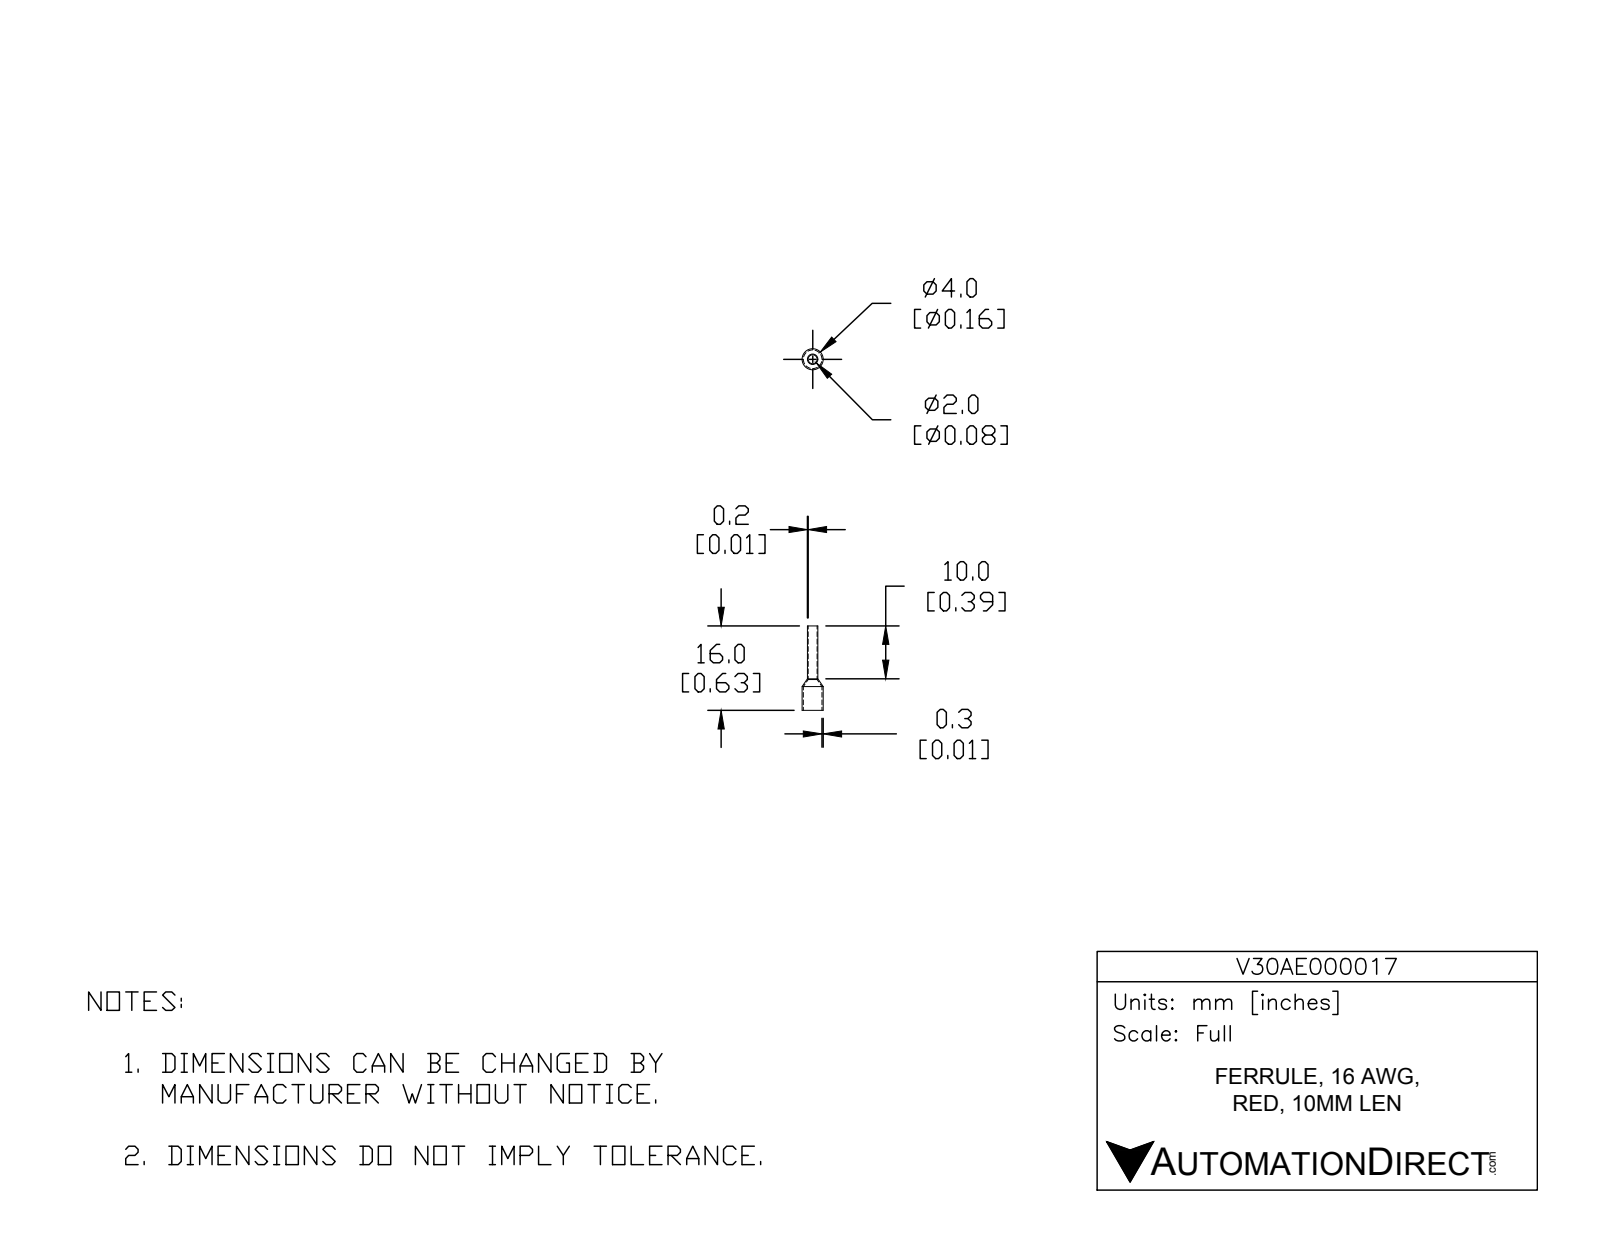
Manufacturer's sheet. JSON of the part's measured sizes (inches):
{"part_name": "V30AE000017", "step_written_by": "SolidWorks 2017 (AUTOMOTIVE_DESIGN)", "units": "inches", "bodies": {"solids": 1, "faces": 14, "planar": 2, "cylindrical": 8, "other": 4}, "overall_size": [0.63, 0.157, 0.157], "volume_in3": 0.002, "surface_area_in2": 0.398, "round_holes": [[0.067, 1], [0.138, 1]], "round_bosses_or_shafts": [[0.157, 1], [0.079, 1]], "face_to_face_distances": [0.63]}
